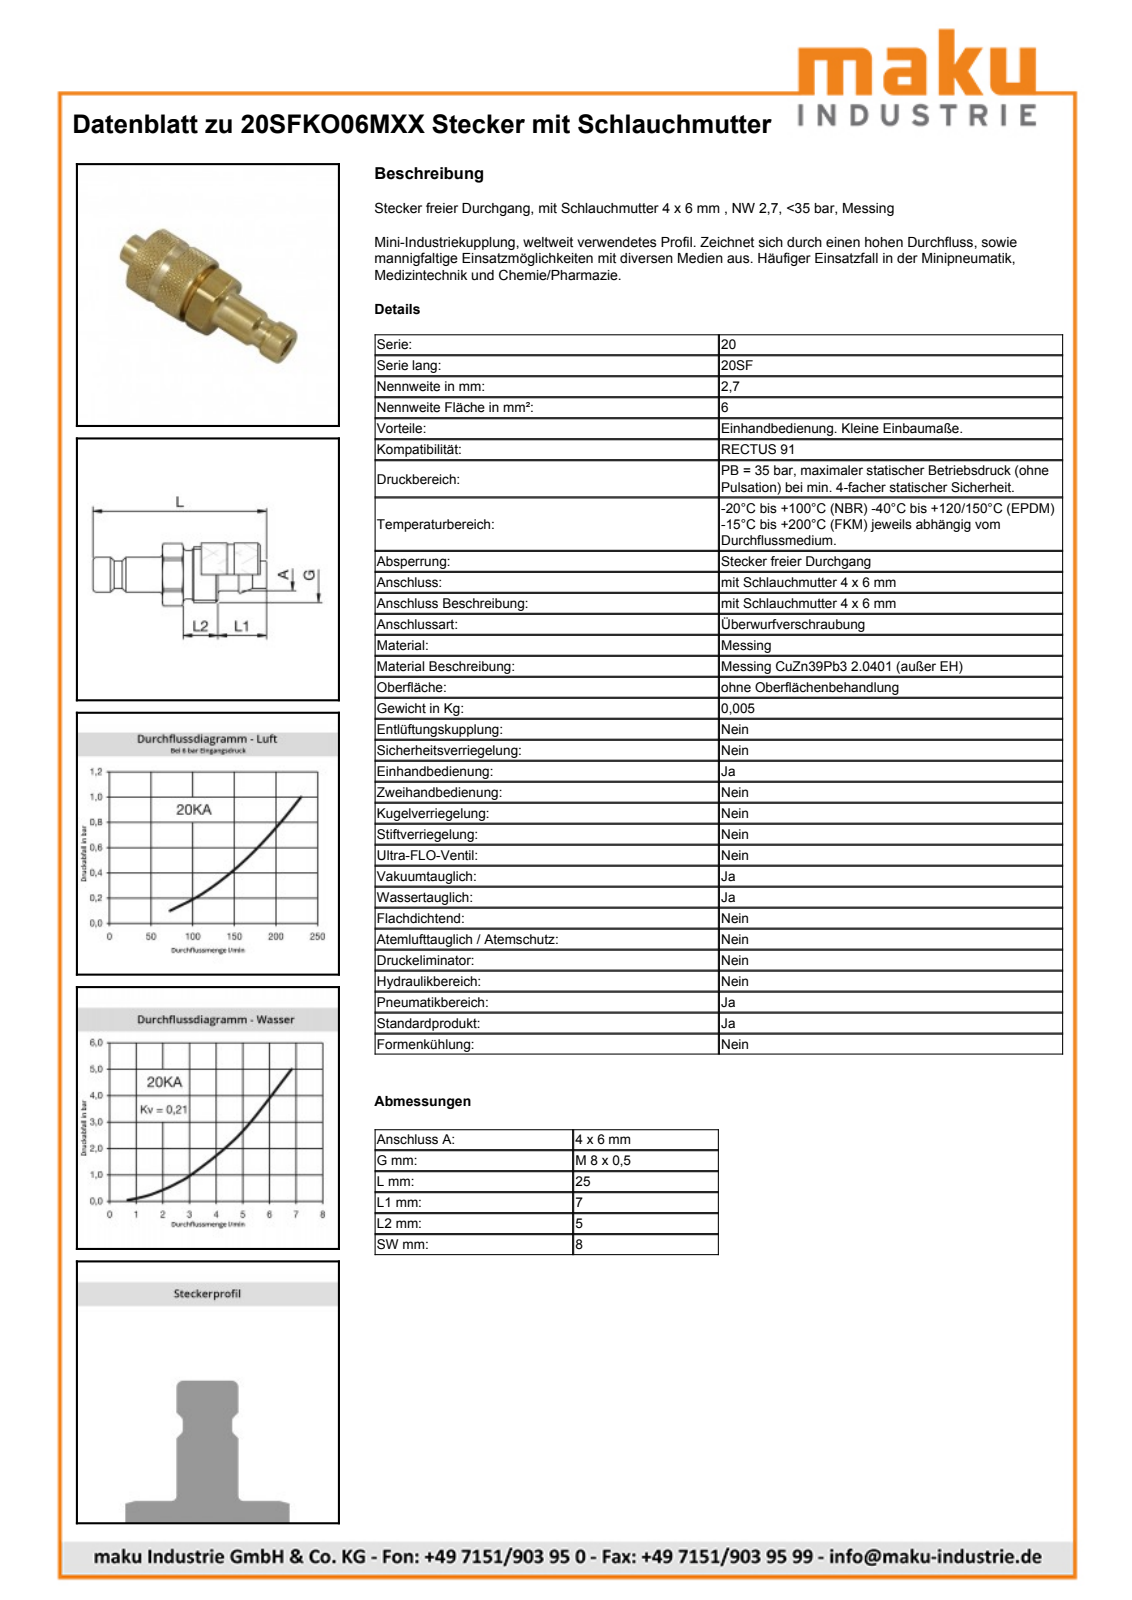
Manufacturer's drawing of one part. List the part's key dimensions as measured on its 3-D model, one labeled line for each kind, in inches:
Part name (STEP PRODUCT): D106366; D106363; D106219
STEP written by: Autodesk Inventor 2011 (AUTOMOTIVE_DESIGN)
Units: inches
Bodies: 2 solids, 66 faces (15 planar, 20 cylindrical, 31 other)
Overall size (bounding box): 0.984 × 0.358 × 0.358
Volume: 0.043 in³ · Surface area: 1.947 in²
Round holes (diameter × count): ⌀0.106 ×1, ⌀0.246 ×1, ⌀0.315 ×1
Round bosses / shafts (diameter × count): ⌀0.358 ×1, ⌀0.343 ×1, ⌀0.283 ×1, ⌀0.276 ×1, ⌀0.197 ×1, ⌀0.177 ×1, ⌀0.156 ×1
Partial cylindrical surfaces — rounded edges, fillets, slot ends (radius × count): R0.177 ×1
Main face-to-face distances: 0.315, 0.492, 0.157, 0.177, 0.148, 0.187, 0.335, 0.394, 0.551, 0.709
